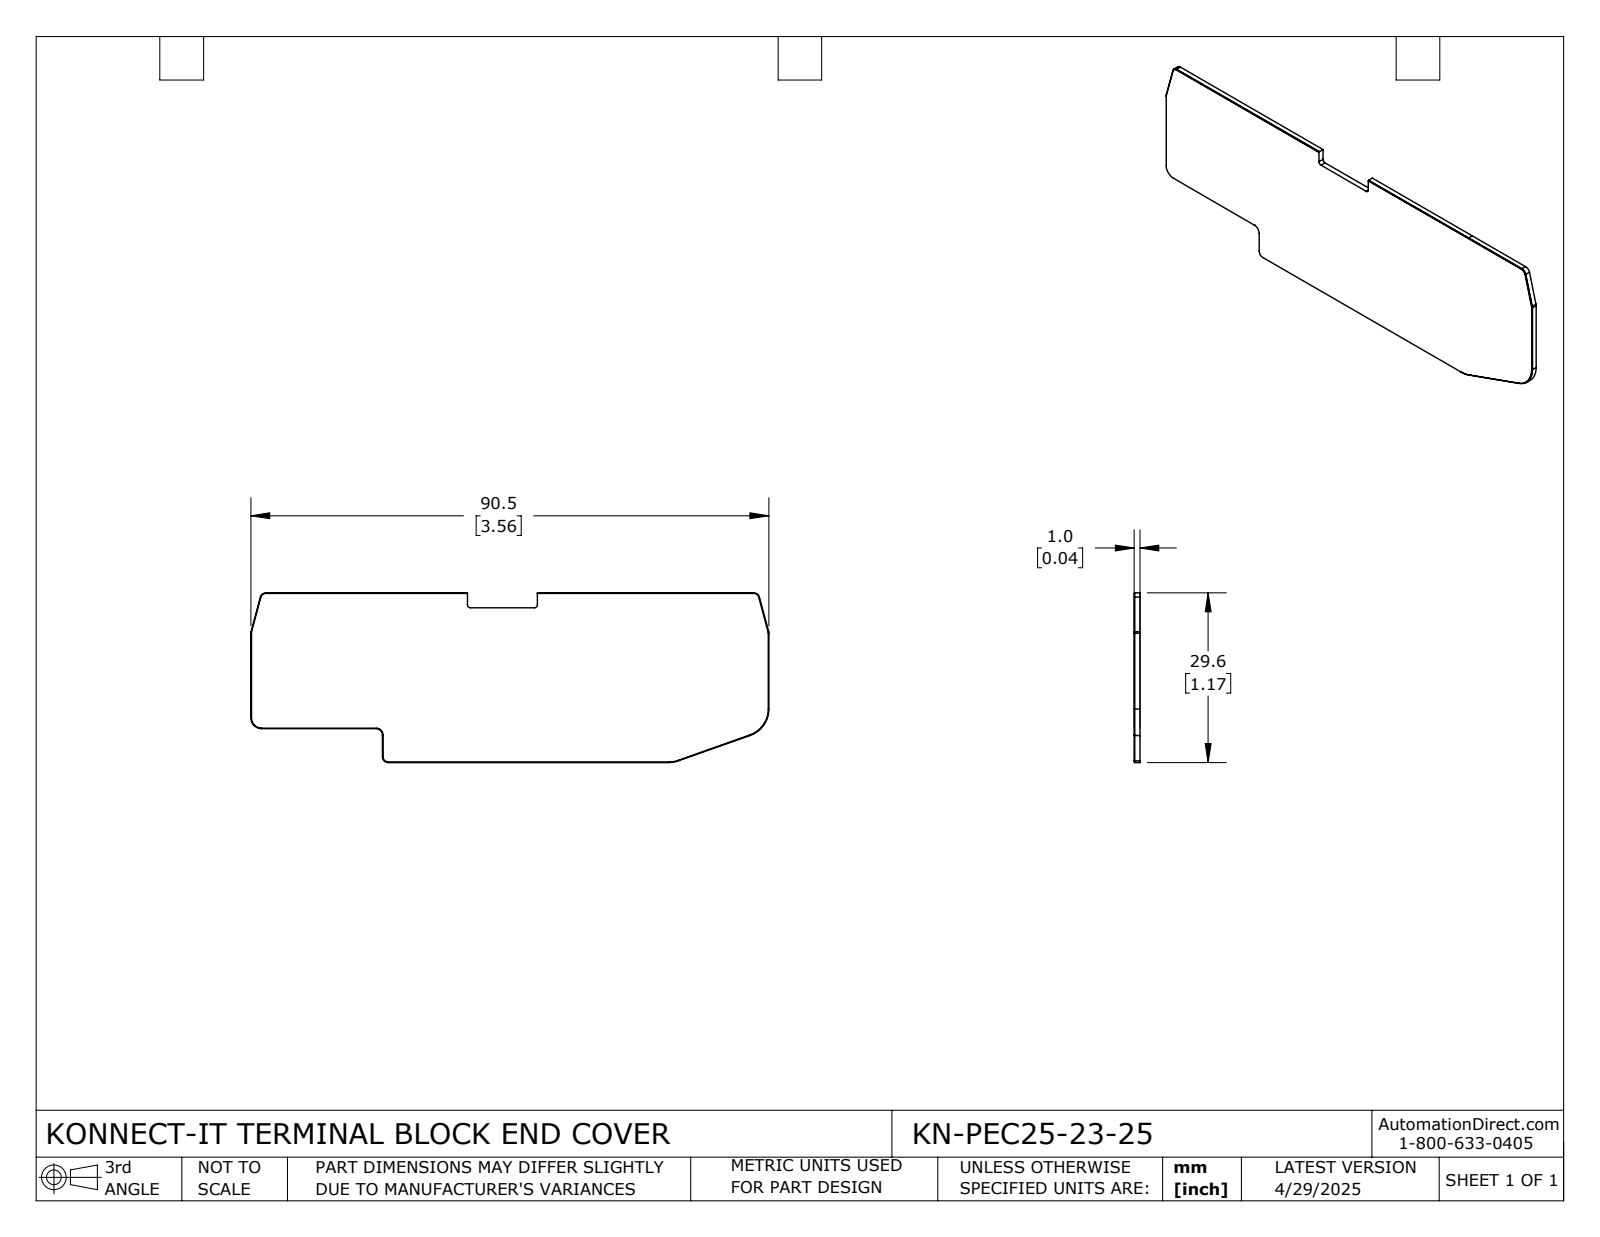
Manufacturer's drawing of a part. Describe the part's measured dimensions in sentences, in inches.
The part is named "KN-PEC25-23-25". Its 3-D file was written by "SolidWorks 2024 (CONFIG_CONTROL_DESIGN)". It is 1 solid with 48 faces: 28 planar, 20 cylindrical and 0 other. Overall it measures 3.561 by 1.166 by 0.039 inches. Its volume is 0.149 cubic inches and its surface area 7.947 square inches. Partial cylindrical surfaces (rounded edges, fillets, slot ends): 5 of radius 0.035, 5 of radius 0.039, 2 of radius 0.02, 2 of radius 0.193, 1 of radius 0.043, 1 of radius 0.047, 1 of radius 0.071, 1 of radius 0.075. The main face-to-face distances are 0.039, 1.166, 0.035, 0.232, 0.934, 1.162, 3.561, 1.064, 0.832, 0.102.
